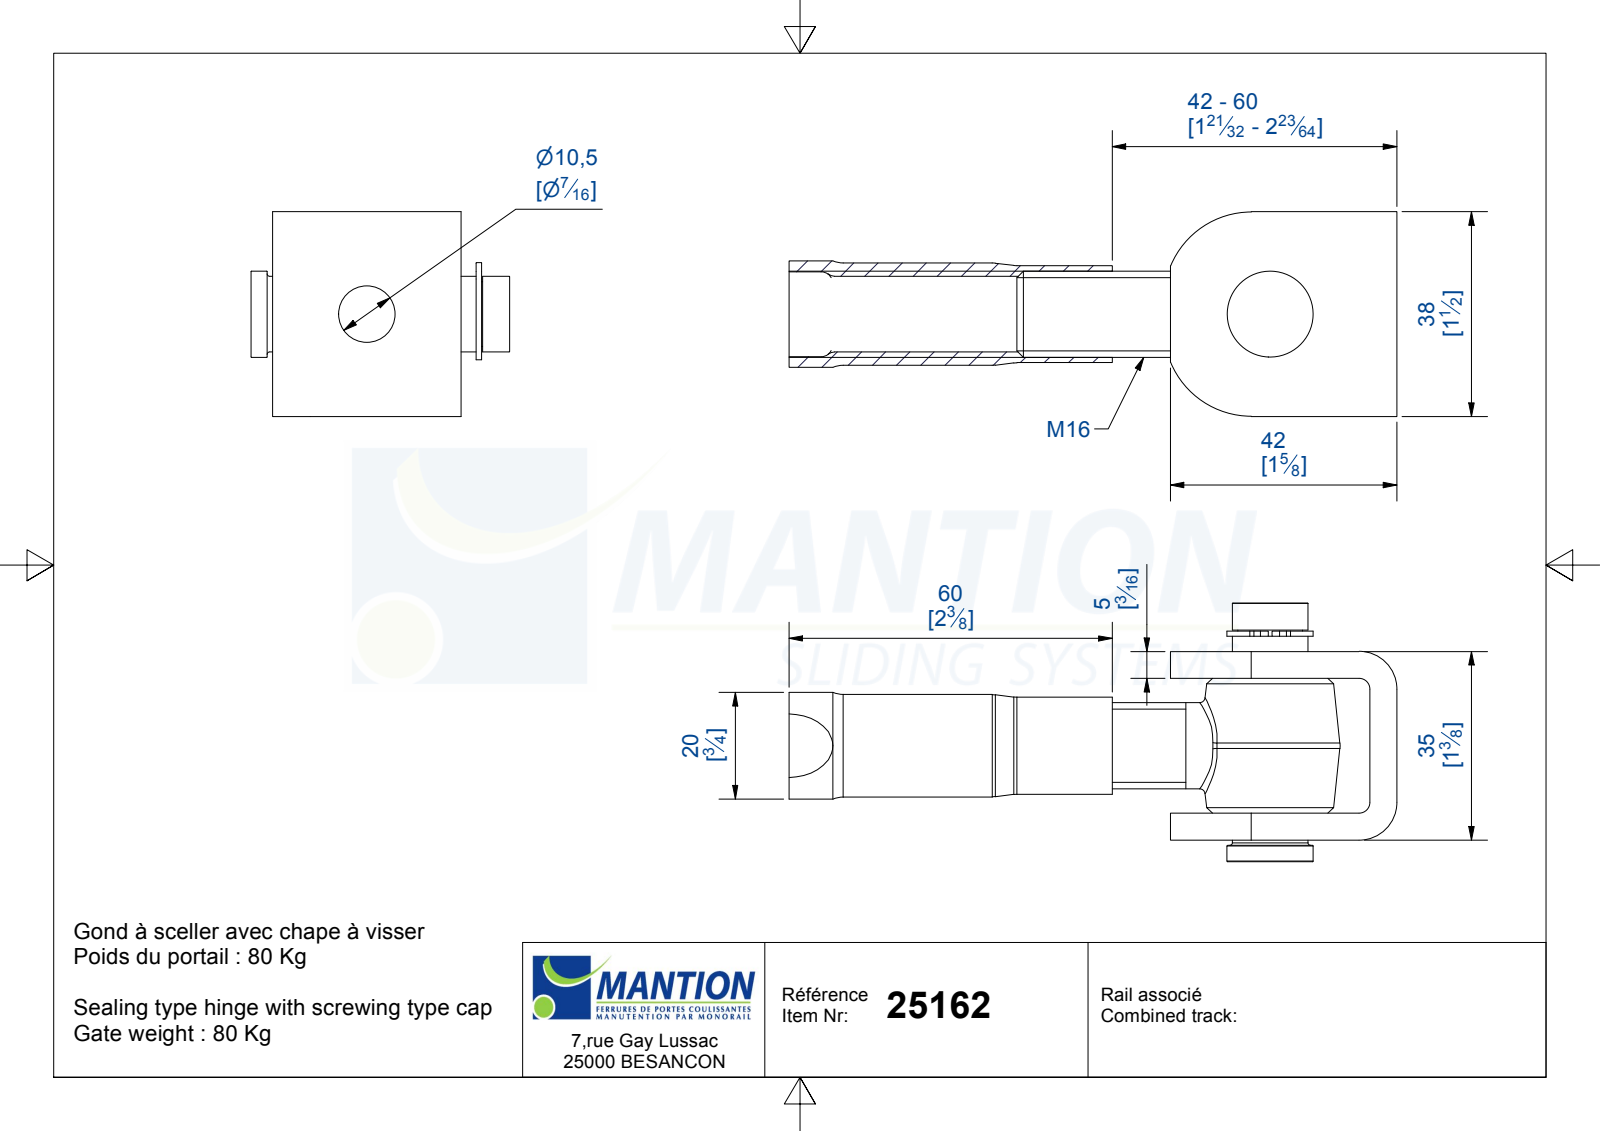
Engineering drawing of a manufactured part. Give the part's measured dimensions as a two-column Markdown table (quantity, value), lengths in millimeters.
| quantity | value |
| --- | --- |
| part name | 25162; 25162-4; 25162-1; 25162-2 (+2 more) |
| STEP written by | Autodesk Inventor 2019 (AUTOMOTIVE_DESIGN) |
| units | millimeters |
| bodies | 5 solids, 128 faces (34 planar, 57 cylindrical, 37 other) |
| overall size | 112.81 × 48 × 38 |
| volume | 45 432 mm³ |
| surface area | 24 763 mm² |
| round holes (diameter × count) | 1.5 × 2, 10.5 × 1, 12.4 × 1, 13.84 × 1, 14.08 × 1, 14.1 × 1, 14.2 × 1 |
| round bosses / shafts (diameter × count) | 16 × 3, 19 × 1, 18 × 1, 14 × 1, 12 × 1 |
| partial cylindrical surfaces (radius × count) | 2 × 6, 1.5 × 4, 3 × 4, 7 × 2, 16.25 × 2, 8.1 × 1, 9.6 × 1 |
| main face-to-face distances | 5, 30, 25, 35, 9, 39, 38, 4, 34, 2 |
| hole center spacings | 8.1, 3 |
